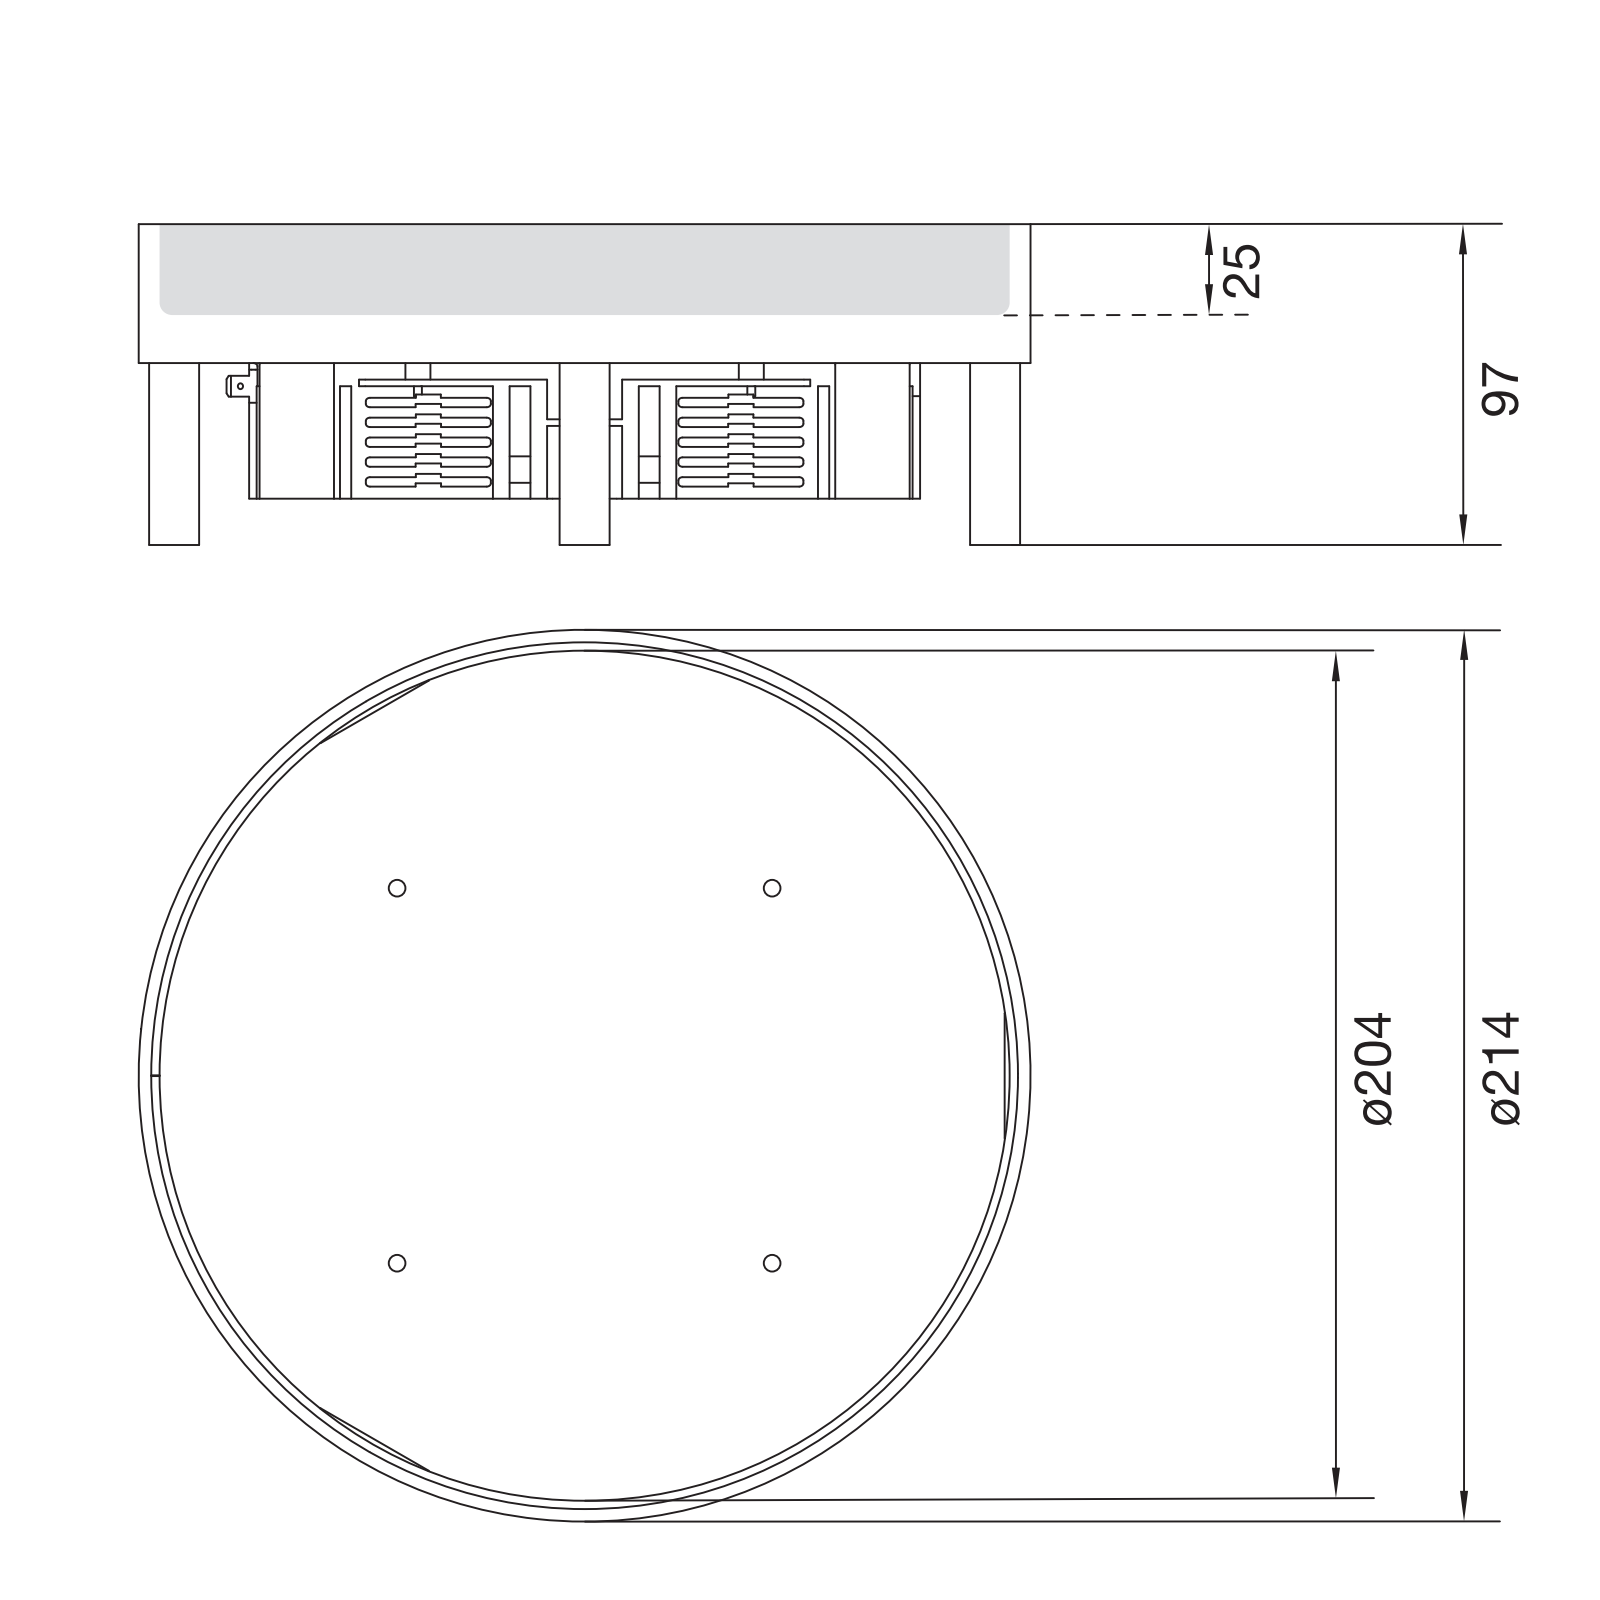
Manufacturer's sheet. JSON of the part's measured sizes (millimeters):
{"part_name": "T-00671; T-00672; T-00673; T-00677 (+8 more)", "step_written_by": "CREO PARAMETRIC BY PTC INC, 2022024 (AUTOMOTIVE_DESIGN)", "units": "millimeters", "bodies": {"solids": 9, "faces": 169, "planar": 97, "cylindrical": 72, "other": 0}, "overall_size": [214, 214, 97], "volume_mm3": 463489, "surface_area_mm2": 329885, "round_holes": [[3.8, 6], [5, 4], [10.1, 4], [117, 1], [210, 1]], "round_bosses_or_shafts": [[12, 4], [9.85, 4], [214, 1], [208, 1], [207, 1], [204, 1]], "partial_cylinders_radius": [[0.5, 8]], "face_to_face_distances": [2, 2.5, 12, 10, 15, 174.5, 153.5, 17, 5, 3], "hole_center_spacings": [69.91, 150.39, 41.16, 44.08, 63.64, 90, 95.62, 97.39]}
